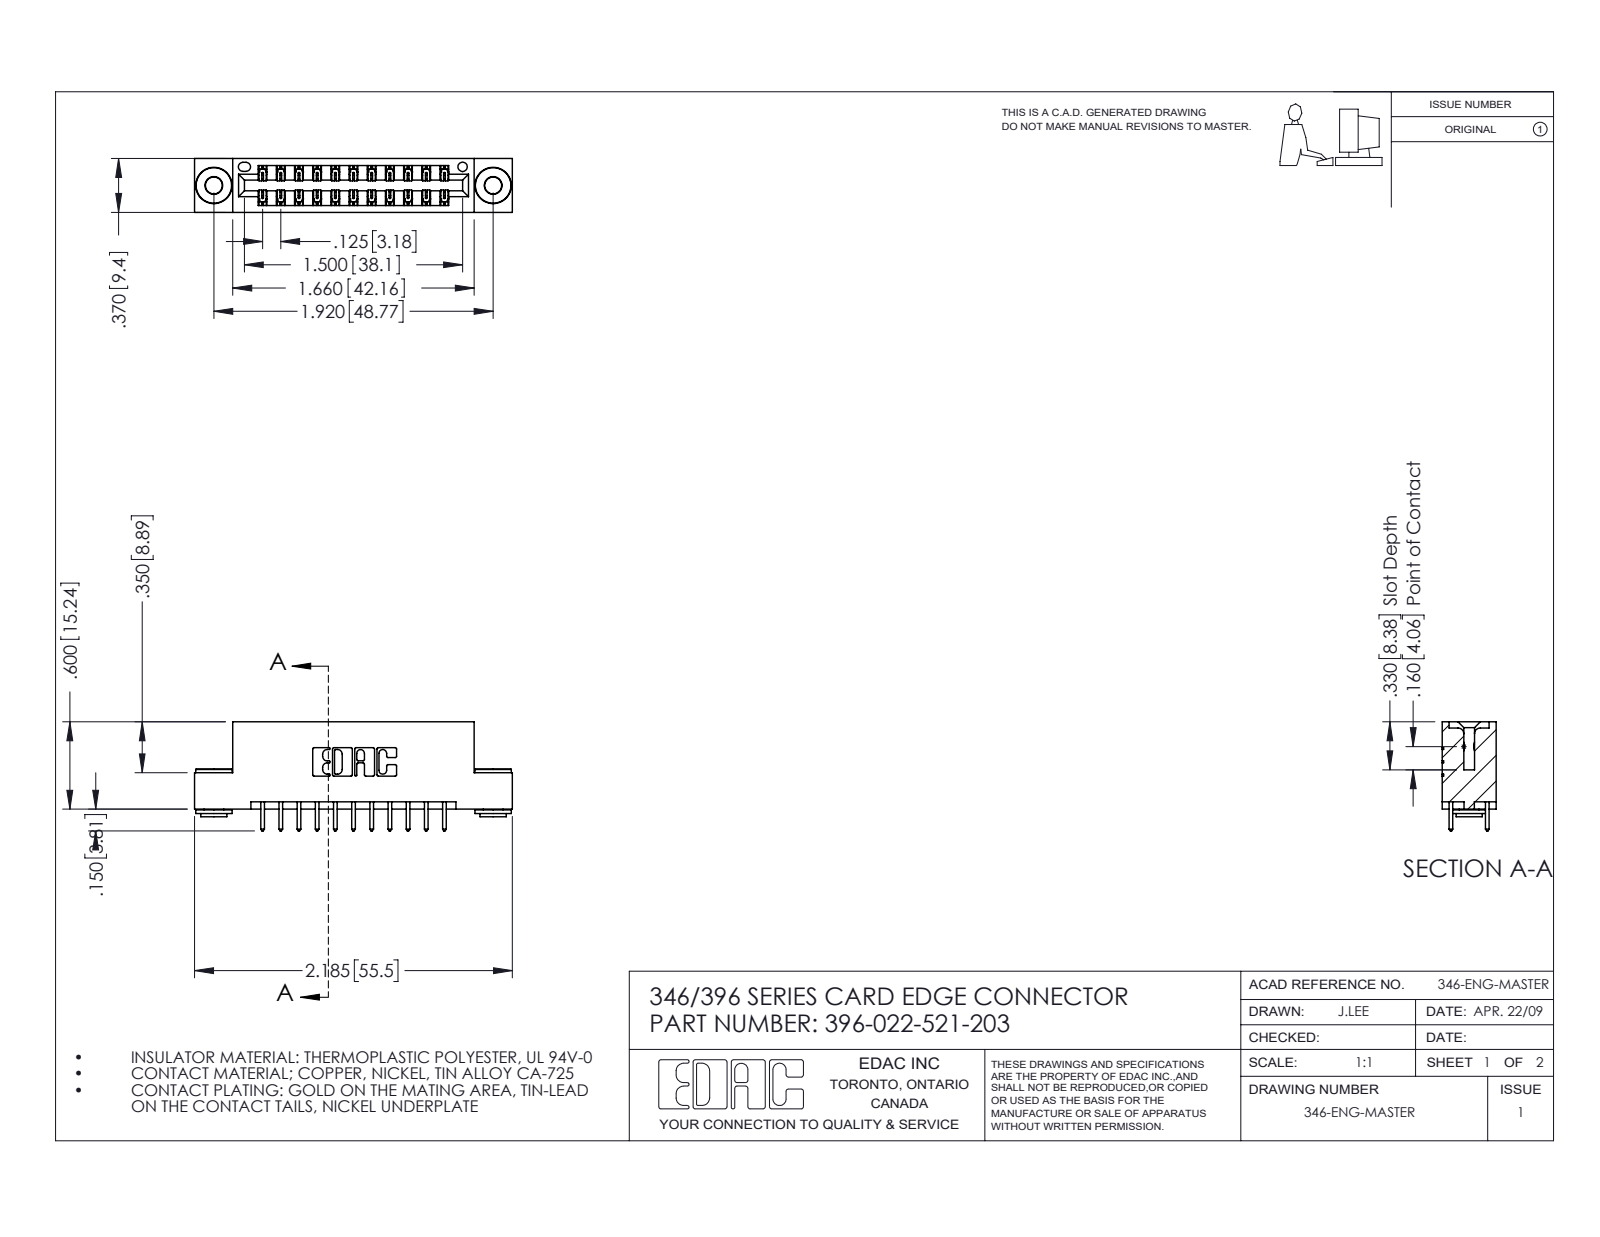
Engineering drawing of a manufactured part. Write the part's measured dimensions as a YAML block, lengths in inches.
part_name: "346 Part_Flush Mounting Lugs - 0.156 Dia-TH; 345-250-002_345-250-002-102; 396-022-521-203; 345-292-001_345-293-121"
step_written_by: "SolidWorks 2016 (CONFIG_CONTROL_DESIGN)"
units: inches
bodies: {solids: 25, faces: 1304, planar: 856, cylindrical: 440, other: 8}
overall_size: [2.185, 0.75, 0.37]
volume: 0.316
surface_area: 10.52
round_holes:
  - {diameter: 0.116, count: 2}
  - {diameter: 0.156, count: 2}
  - {diameter: 0.064, count: 1}
round_bosses_or_shafts:
  - {diameter: 0.25, count: 2}
  - {diameter: 0.18, count: 2}
  - {diameter: 0.136, count: 2}
partial_cylinders:
  - {radius: 0.006, count: 33}
  - {radius: 0.01, count: 22}
  - {radius: 0.01, count: 22}
  - {radius: 0.007, count: 6}
  - {radius: 0.031, count: 6}
  - {radius: 0.026, count: 3}
  - {radius: 0.014, count: 2}
  - {radius: 0.022, count: 2}
face_to_face_distances: [0.25, 0.048, 0.322, 0.37, 0.025, 0.072, 0.298, 0.275, 0.148, 0.222]
hole_center_spacings: [0.246, 1.715, 1.92]
